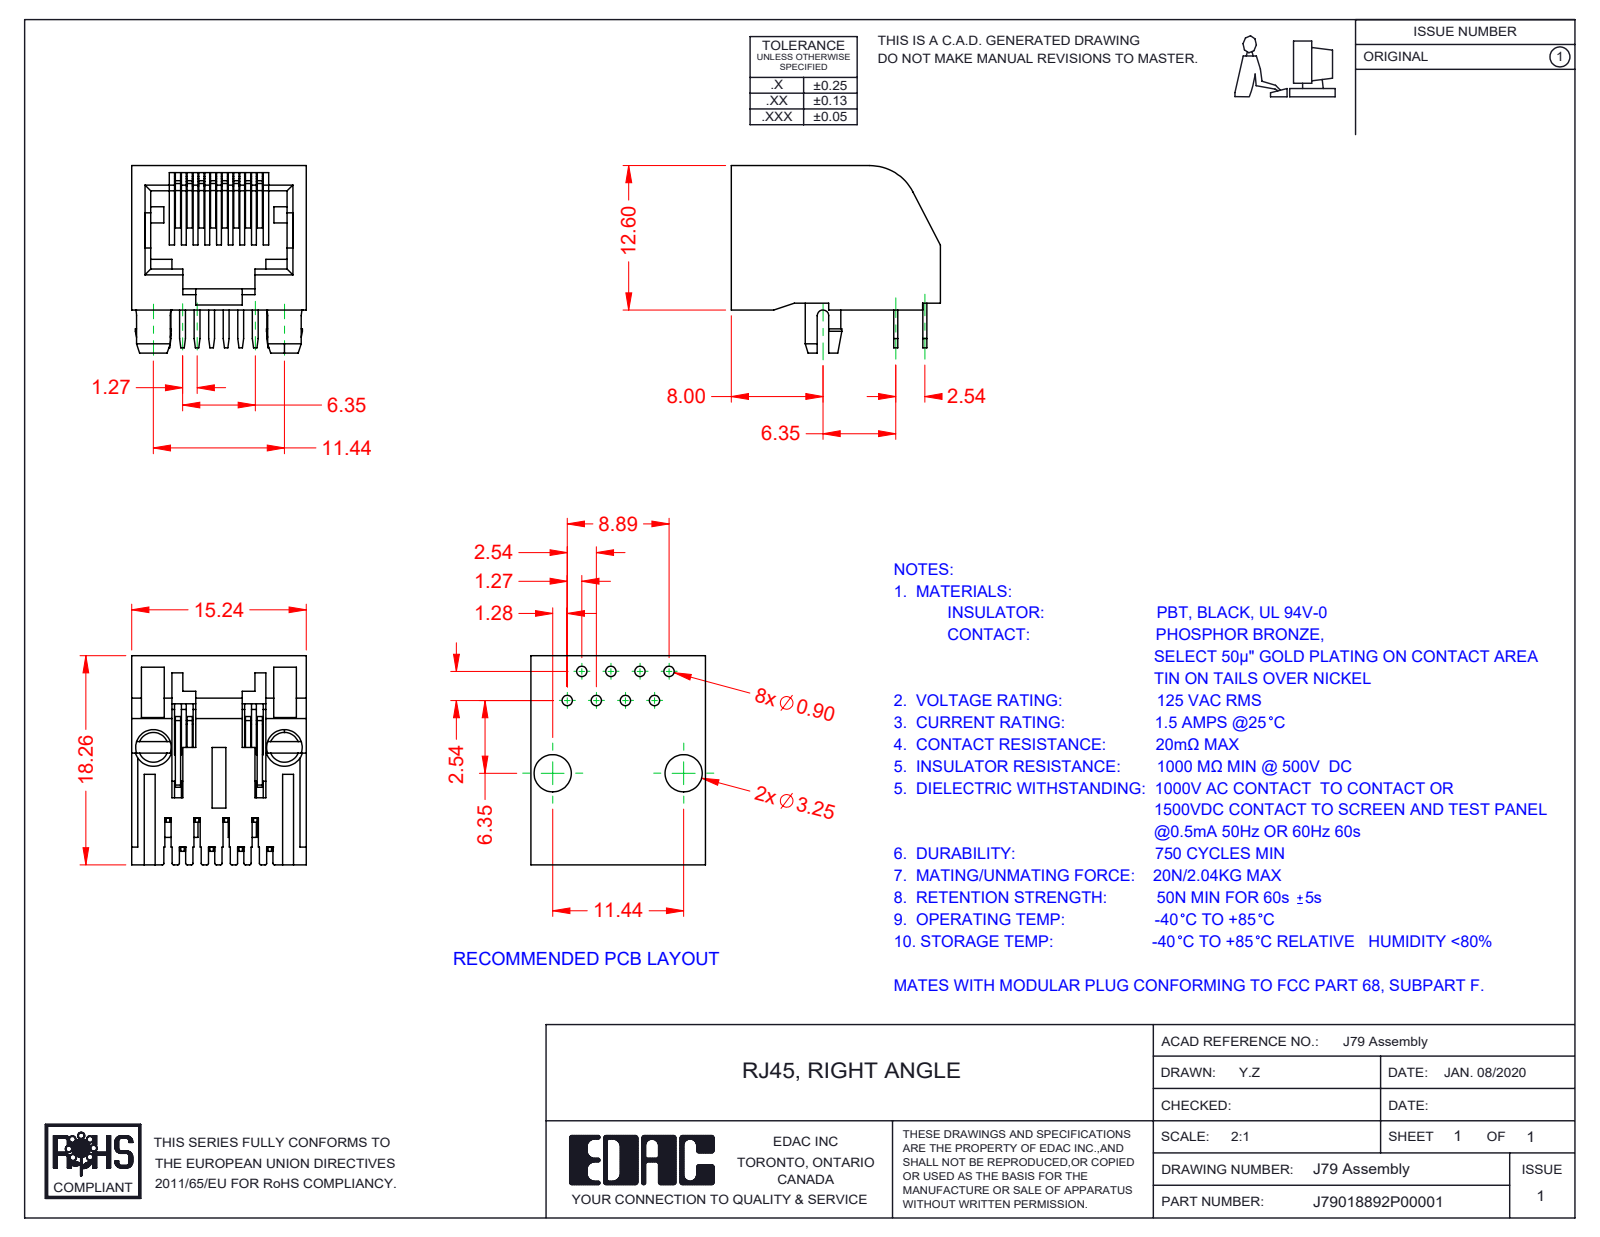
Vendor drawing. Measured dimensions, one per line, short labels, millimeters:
name: RJ79018892P00001; 79 Contacts; 79 Insulator
written by: SolidWorks 2016 (CONFIG_CONTROL_DESIGN)
unit: mm
bodies: 9 solids, 574 faces (424 planar, 144 cylindrical, 6 other)
size: 18.26 × 16.36 × 15.24
volume: 1 496 mm³; area: 3 263 mm²
bosses: 2× ⌀3.1
rounds: 16× R0.15, 7× R0.5, 3× R0.72, 2× R0.36, 2× R1.65, 2× R1.8, 2× R2.16, 1× R0.2
face distances: 15.24, 2.04, 0.6, 12, 0.36, 4.08, 1.25, 9.8, 2.2, 8.2
